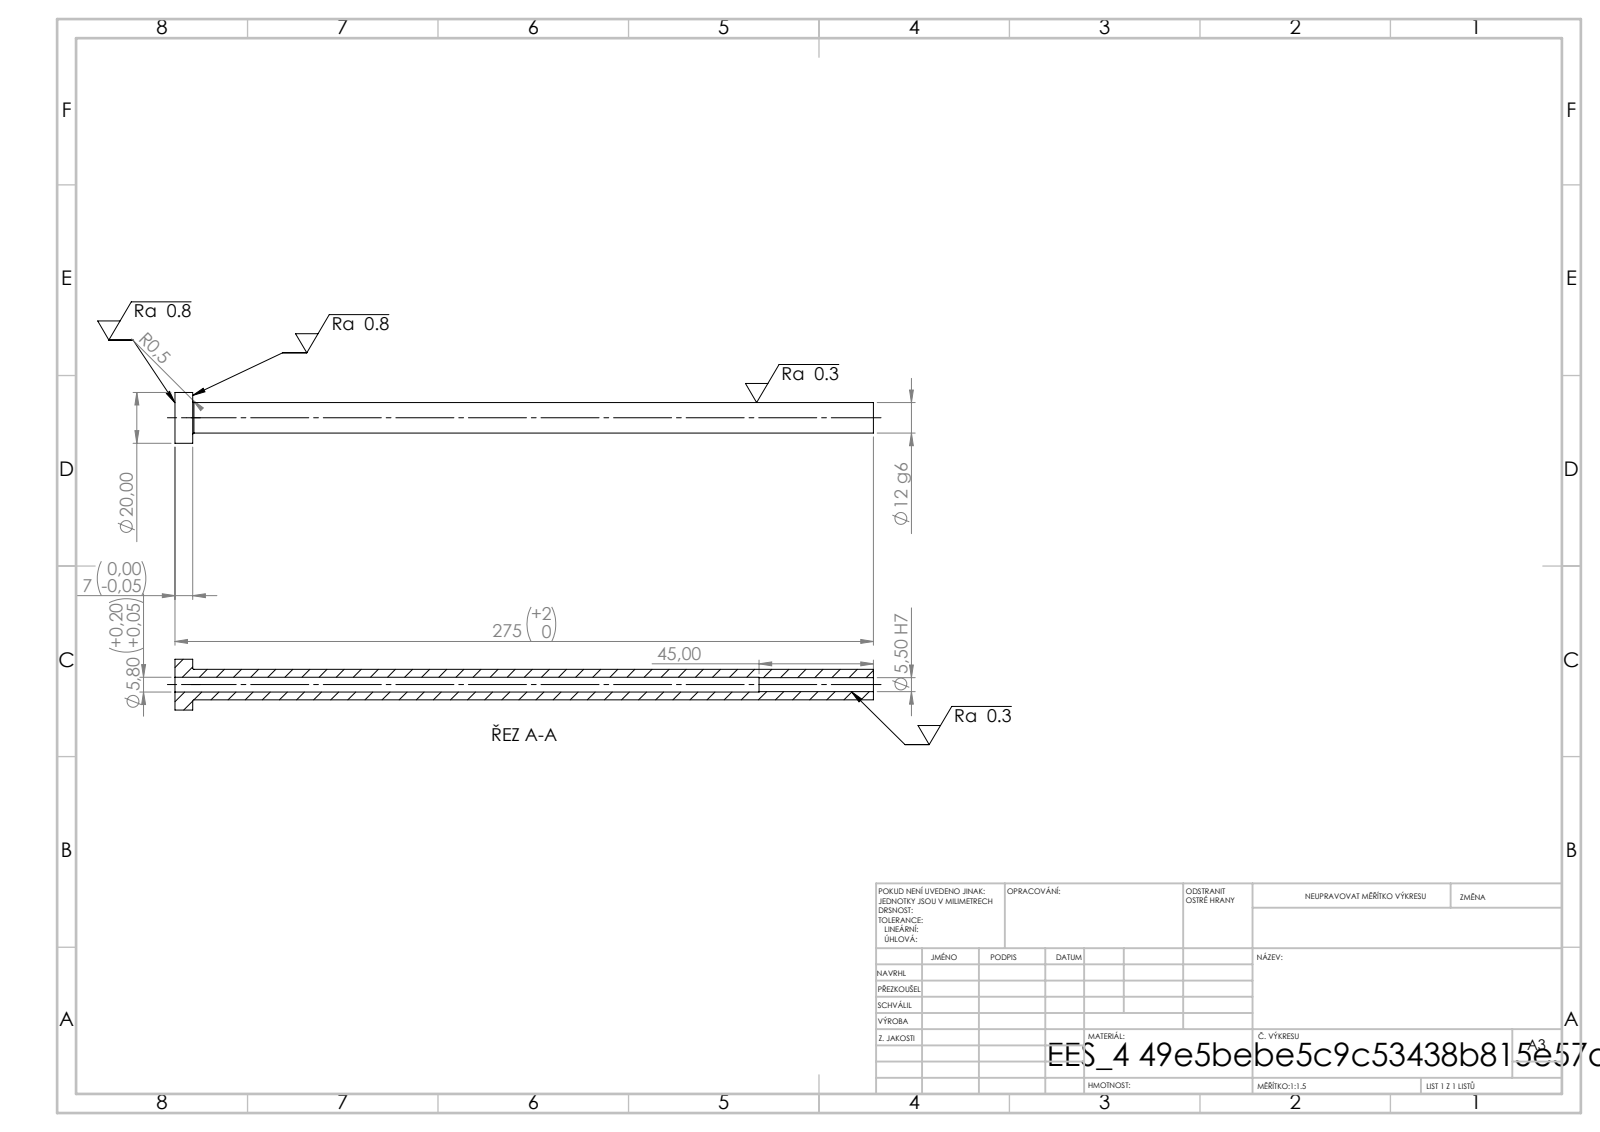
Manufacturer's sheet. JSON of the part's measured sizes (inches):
{"step_written_by": "SolidWorks 2019 (CONFIG_CONTROL_DESIGN)", "units": "inches", "bodies": {"solids": 1, "faces": 14, "planar": 4, "cylindrical": 8, "other": 2}, "overall_size": [10.827, 0.787, 0.787], "volume_in3": 1.548, "surface_area_in2": 24.93, "round_holes": [[0.217, 1], [0.228, 1]], "round_bosses_or_shafts": [[0.787, 1], [0.472, 1]], "face_to_face_distances": [0.276, 10.827, 10.551, 9.055, 8.78, 1.772]}
